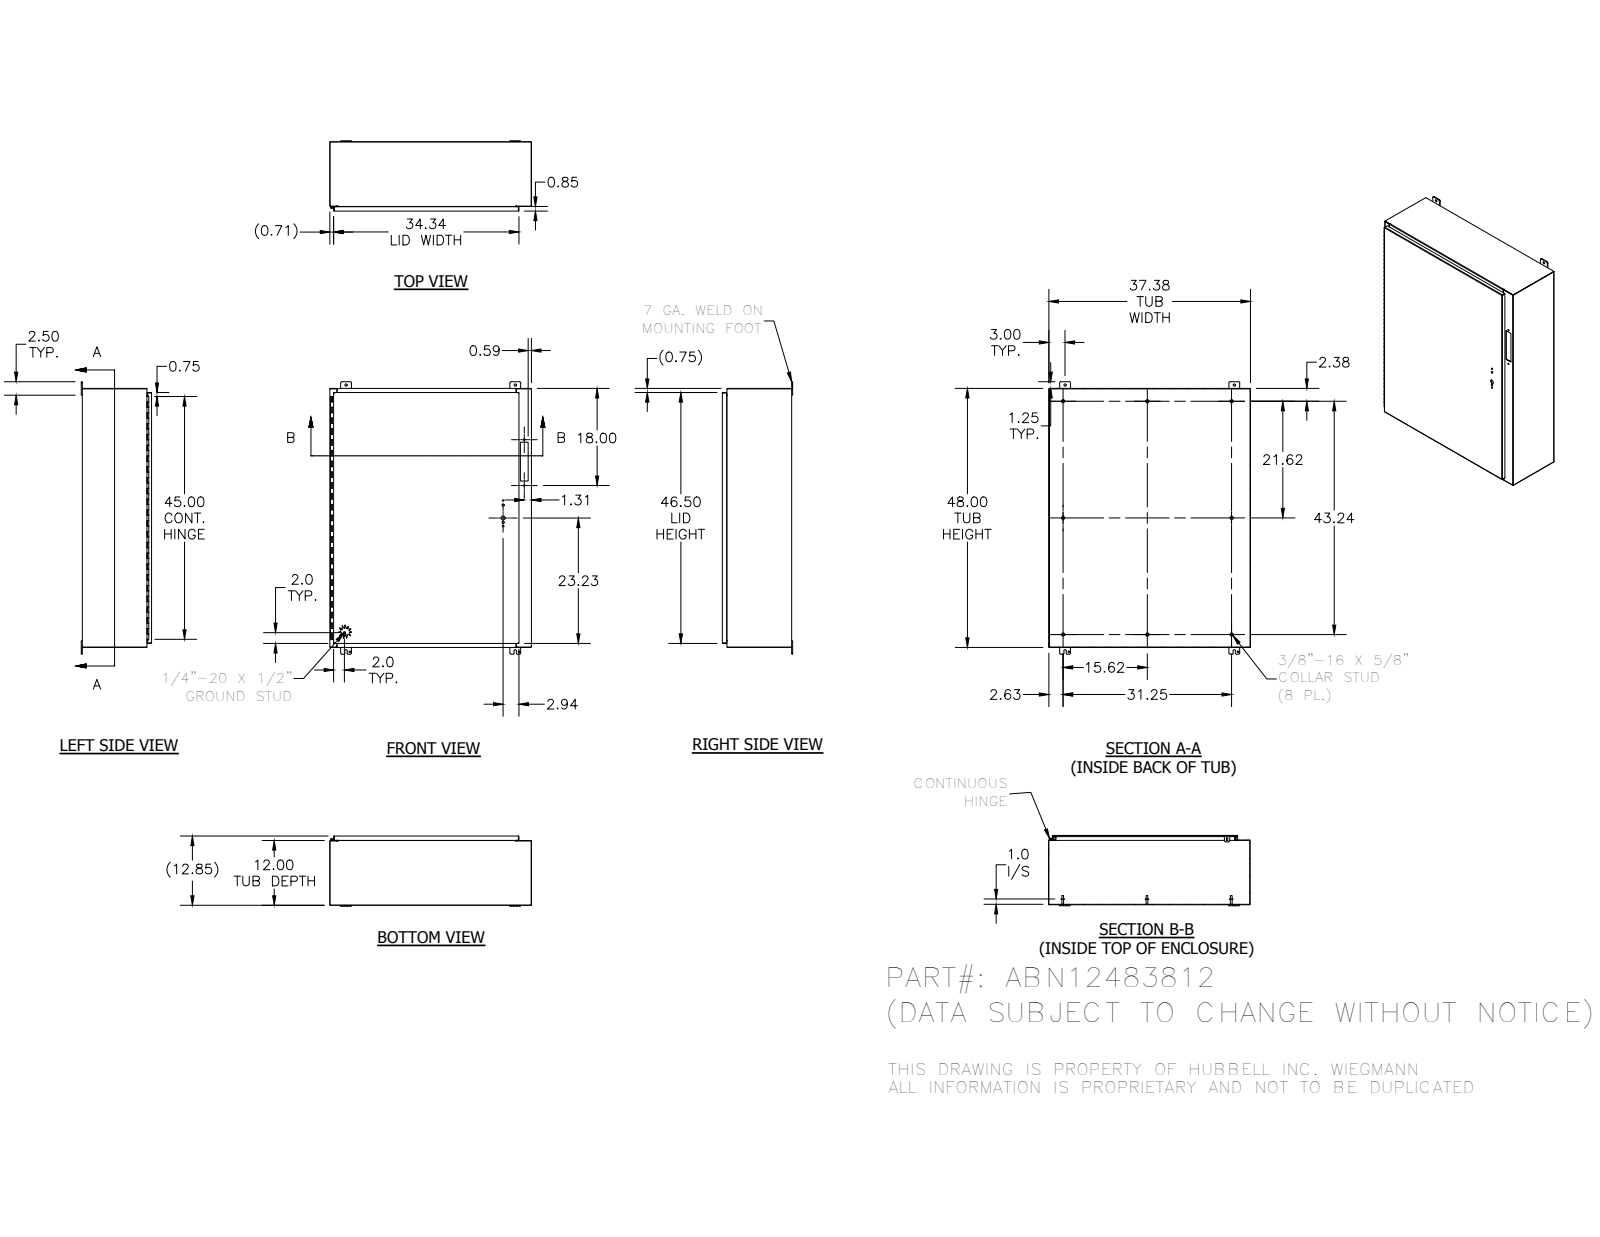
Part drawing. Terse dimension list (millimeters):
name: ABN12483812BLR; 3889; 34840; 328115T (+8 more)
written by: Autodesk Inventor 2014 (AUTOMOTIVE_DESIGN)
unit: mm
bodies: 27 solids, 859 faces (544 planar, 269 cylindrical, 46 other)
size: 1282.7 × 949.33 × 330.86
volume: 7 344 000 mm³; area: 7 843 000 mm²
holes: 4× ⌀7.14, 4× ⌀7.95, 4× ⌀11.13, 2× ⌀3.96, 2× ⌀10.31, 1× ⌀3.17, 1× ⌀19.05
bosses: 9× ⌀8.38, 8× ⌀15.88, 4× ⌀6.35, 2× ⌀4.83, 1× ⌀8.56, 1× ⌀3.05
rounds: 18× R0.79, 18× R2.67, 18× R6.35, 8× R3.17, 6× R1.52, 4× R5.56, 3× R1.59, 2× R0.38
face distances: 1.88, 324.41, 322.53, 326.29, 947.45, 1217.32, 949.33, 945.57, 21.49, 302.92
hole spacings: 40.46, 796.92, 1219.2, 1456.55, 780.32, 815.19, 1182.83, 1255.82
